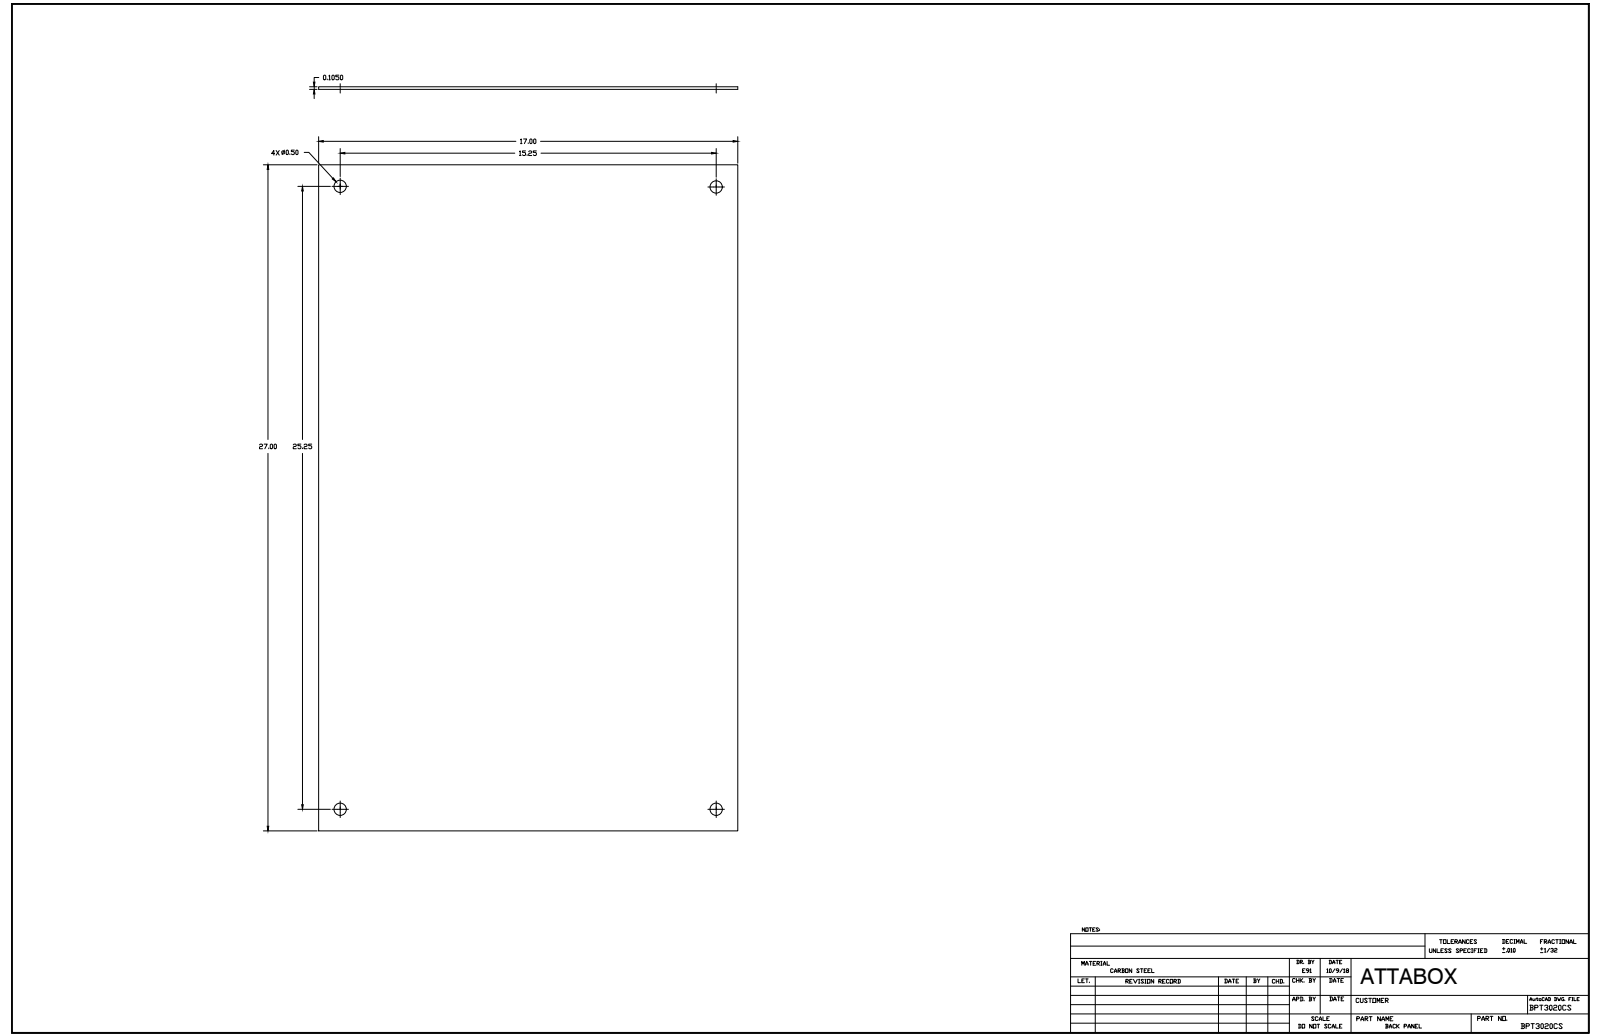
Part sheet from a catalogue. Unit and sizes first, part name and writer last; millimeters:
Units: millimetres
Overall size (bounding box): 685.8 × 431.8 × 2.67
Round holes (diameter × count): ⌀12.7 ×4
Main face-to-face distances: 2.66, 431.8, 685.8
Hole centre spacings: 387.34, 641.34, 749.23
Volume: 788 423 mm³ · Surface area: 597 630 mm²
Bodies: 1 solid, 10 faces (6 planar, 4 cylindrical, 0 other)
Part name (STEP PRODUCT): BP3020CS_STP
STEP written by: Autodesk Inventor 2014 (AUTOMOTIVE_DESIGN)
